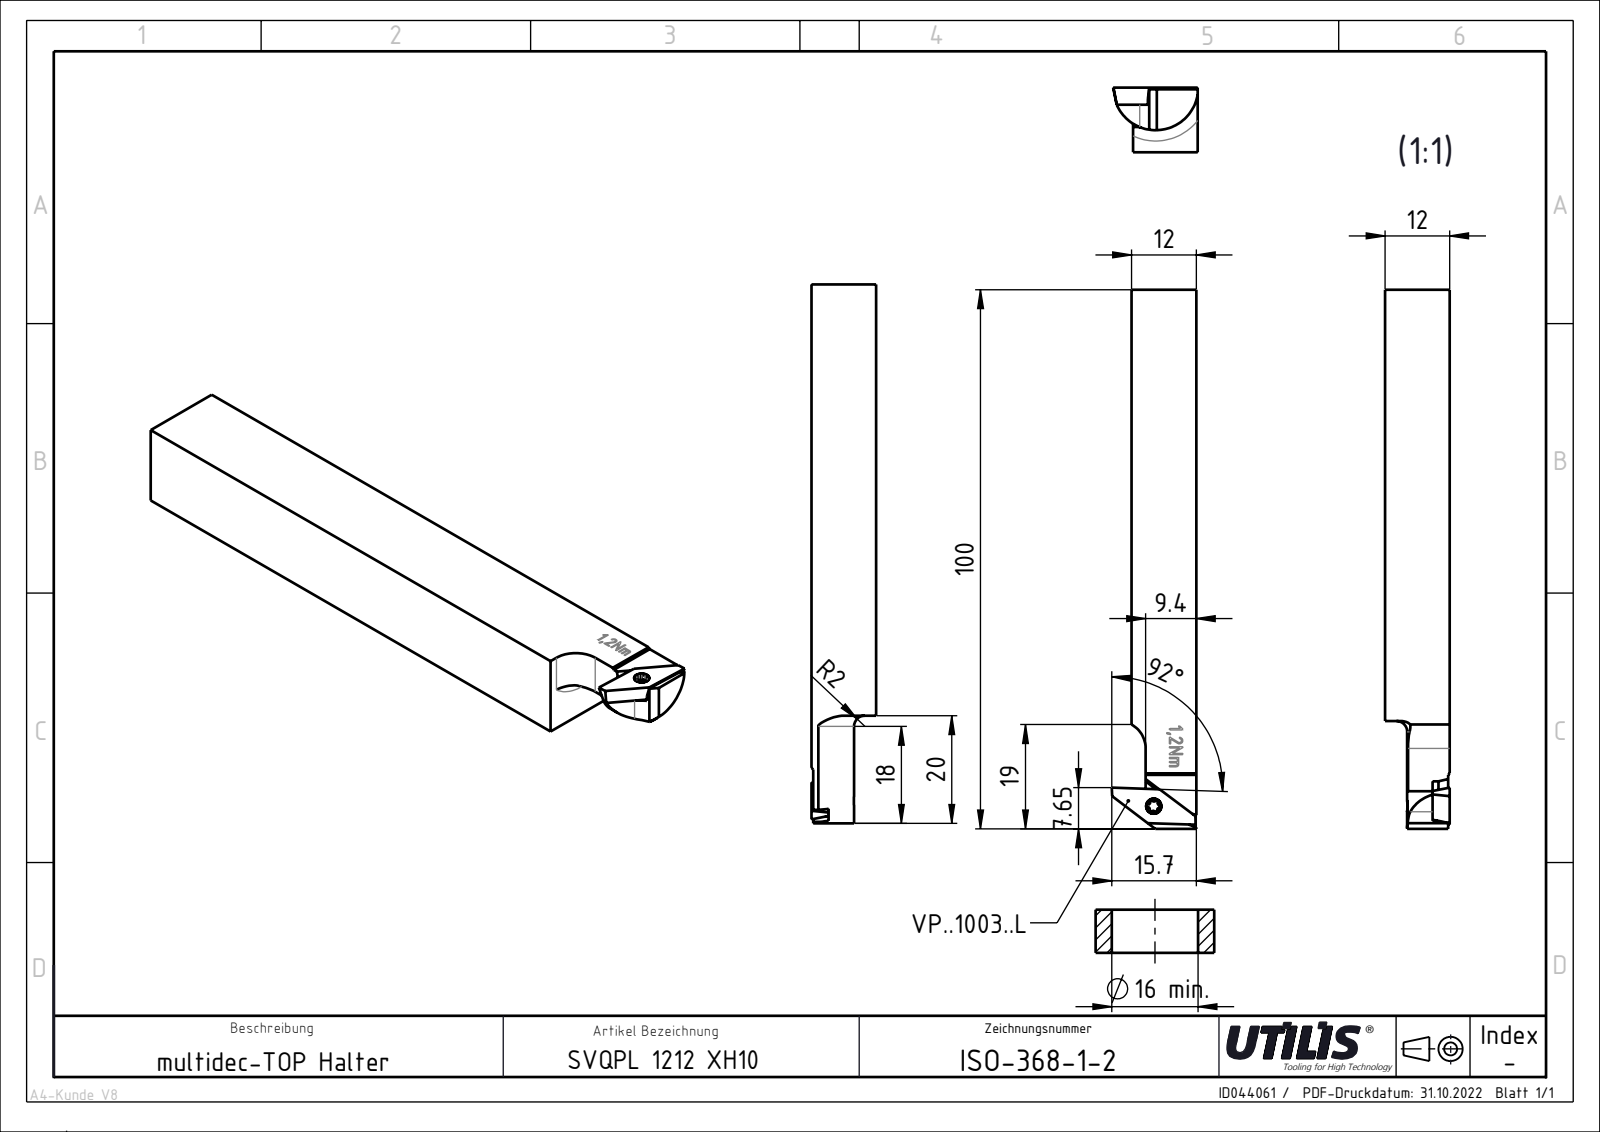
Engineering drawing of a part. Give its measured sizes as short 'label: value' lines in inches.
name: ISO-368-1_WSP_10036; ISO-368-1_2; ISO-368-1-2
written by: SolidWorks 2022 (CONFIG_CONTROL_DESIGN)
unit: in
bodies: 2 solids, 35 faces (30 planar, 4 cylindrical, 1 other)
size: 3.937 × 0.617 × 0.472
volume: 0.784 in³; area: 7.81 in²
holes: 1× ⌀0.11
rounds: 1× R0.201, 1× R0.24, 1× R0.311
face distances: 0.472, 0.347, 0.125, 0.102, 0.37, 0.461, 0.113, 3.937, 0.787, 3.15
